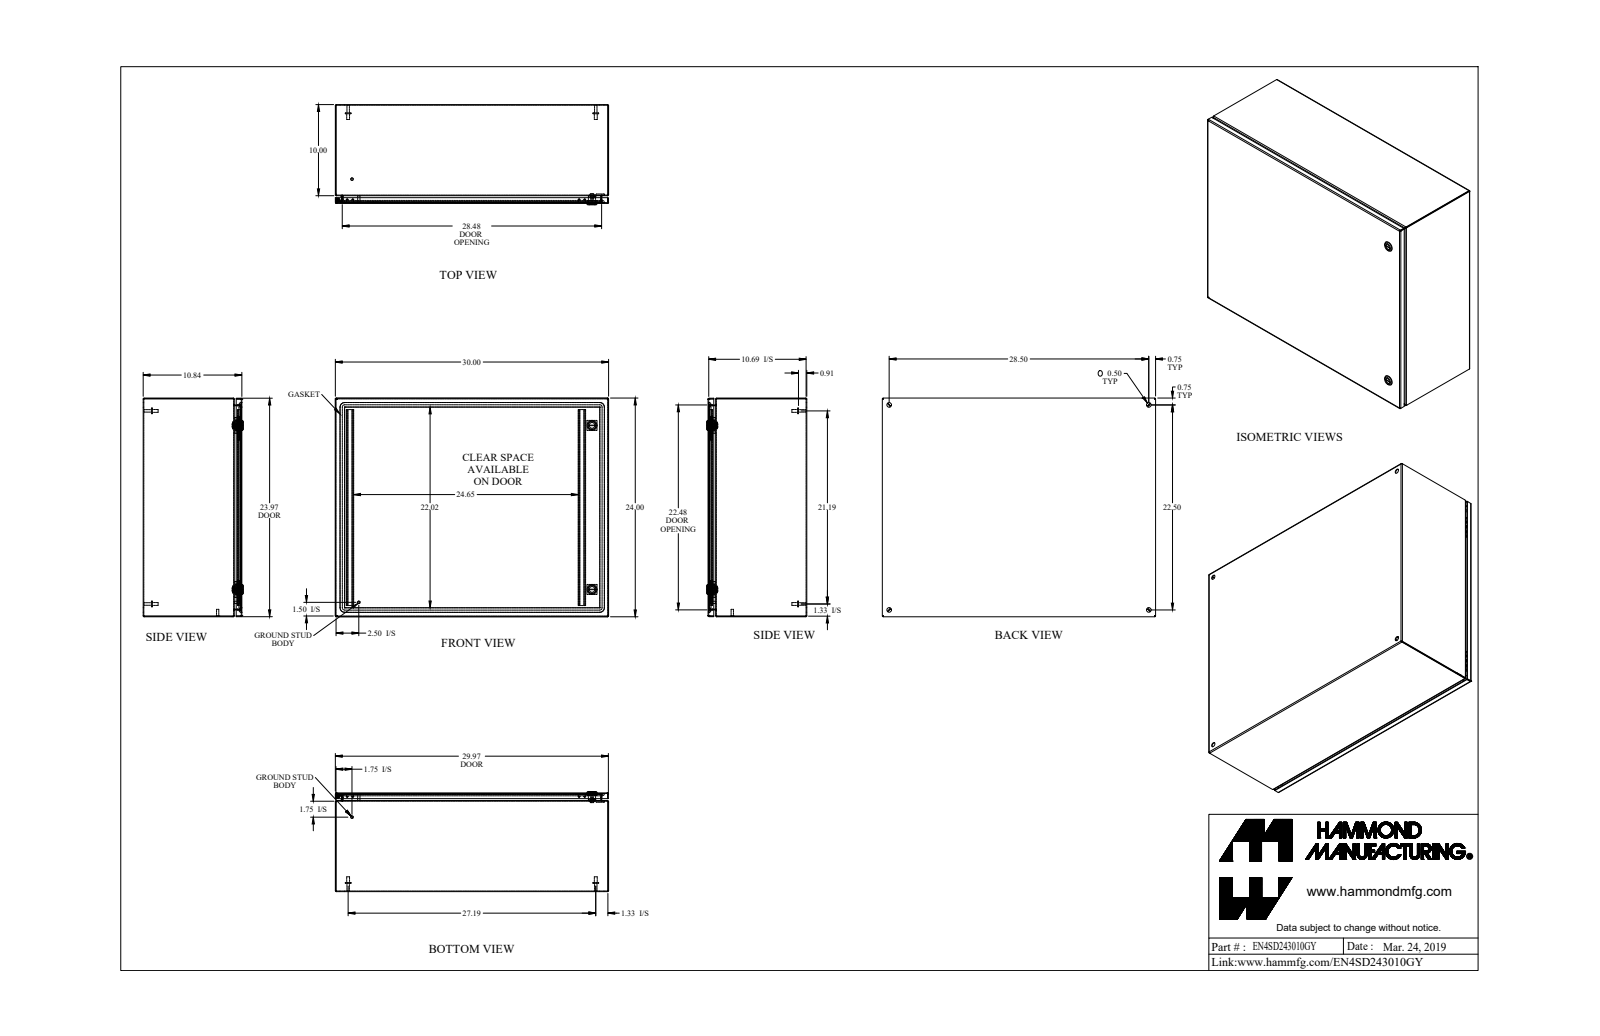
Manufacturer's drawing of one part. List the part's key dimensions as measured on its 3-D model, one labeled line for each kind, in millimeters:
Part name (STEP PRODUCT): EN4SD243010GY
STEP written by: SolidWorks 2019 (AUTOMOTIVE_DESIGN)
Units: millimetres
Bodies: 27 solids, 752 faces (359 planar, 257 cylindrical, 136 other)
Overall size (bounding box): 762 × 609.6 × 279.3
Volume: 3 438 000 mm³ · Surface area: 3 782 000 mm²
Round holes (diameter × count): ⌀12.7 ×4, ⌀5.9 ×2, ⌀15.9 ×2, ⌀19.9 ×2, ⌀4.4 ×1, ⌀6.1 ×1, ⌀6.1 ×1
Round bosses / shafts (diameter × count): ⌀15.9 ×4, ⌀8 ×4, ⌀6.9 ×4, ⌀27.9 ×2, ⌀13.3 ×2, ⌀7.1 ×2, ⌀6.4 ×2, ⌀11.6 ×1
Partial cylindrical surfaces — rounded edges, fillets, slot ends (radius × count): R0.9 ×16, R2.7 ×16, R1.1 ×12, R2.1 ×12, R9.7 ×12, R2.5 ×8, R482.7 ×8, R0.2 ×4
Main face-to-face distances: 1.8, 273.4, 271.6, 275.3, 607.8, 760.2, 605.9, 609.6, 758.3, 762
Hole centre spacings: 571.5, 699, 723.9, 922.3, 63.3, 63.3, 457.2, 515
